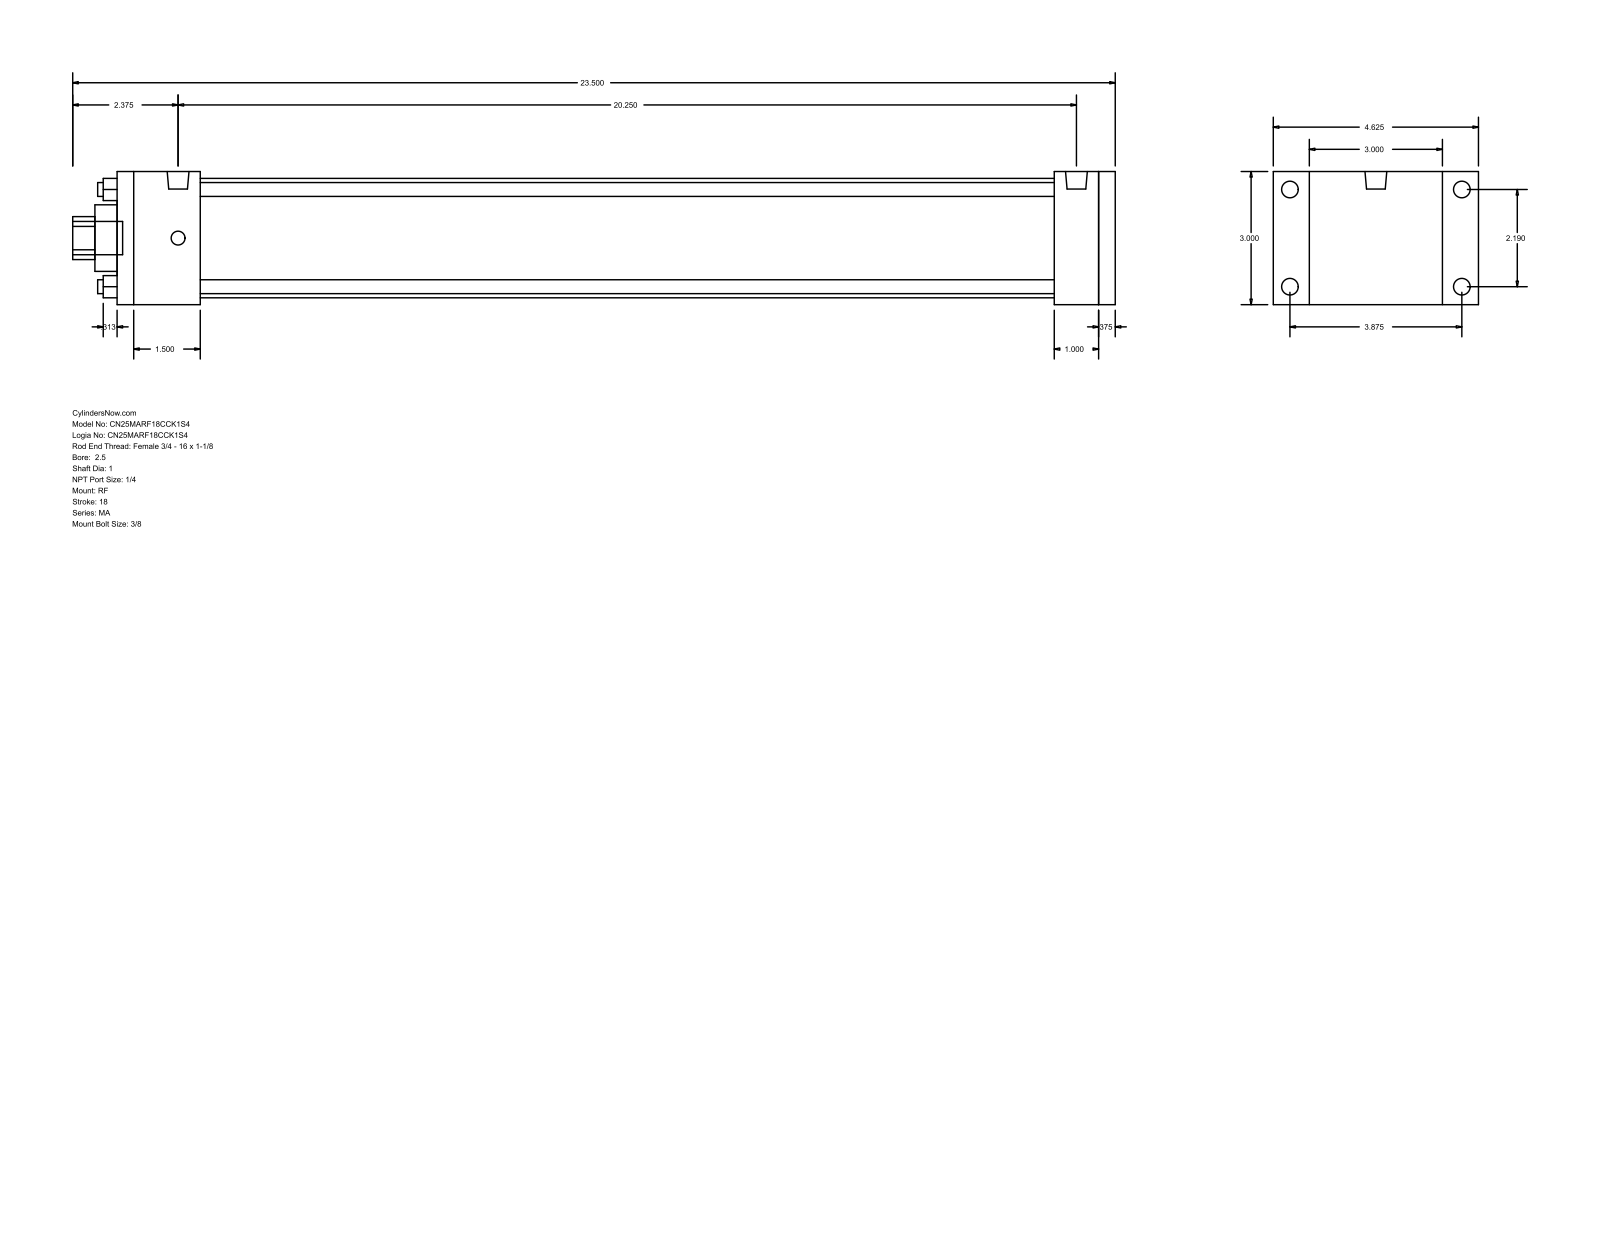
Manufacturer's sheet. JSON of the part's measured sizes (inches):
{"part_name": "MA_RF__0250_1", "step_written_by": "GSSL Pune (CONFIG_CONTROL_DESIGN)", "units": "inches", "bodies": {"solids": 0, "faces": 92, "planar": 64, "cylindrical": 28, "other": 0}, "overall_size": [23.5, 4.625, 3], "round_holes": [[0.313, 4], [1, 1], [1.5, 1], [2.69, 1]], "round_bosses_or_shafts": [[0.375, 4], [0.313, 4], [0.492, 2], [0.75, 1]], "partial_cylinders_radius": [[0.484, 1]], "face_to_face_distances": [3, 22.5, 22.125, 0.375, 1, 1.875, 21.125, 19.25, 20.25, 20.625], "hole_center_spacings": [1.548, 2.19, 3.097]}
